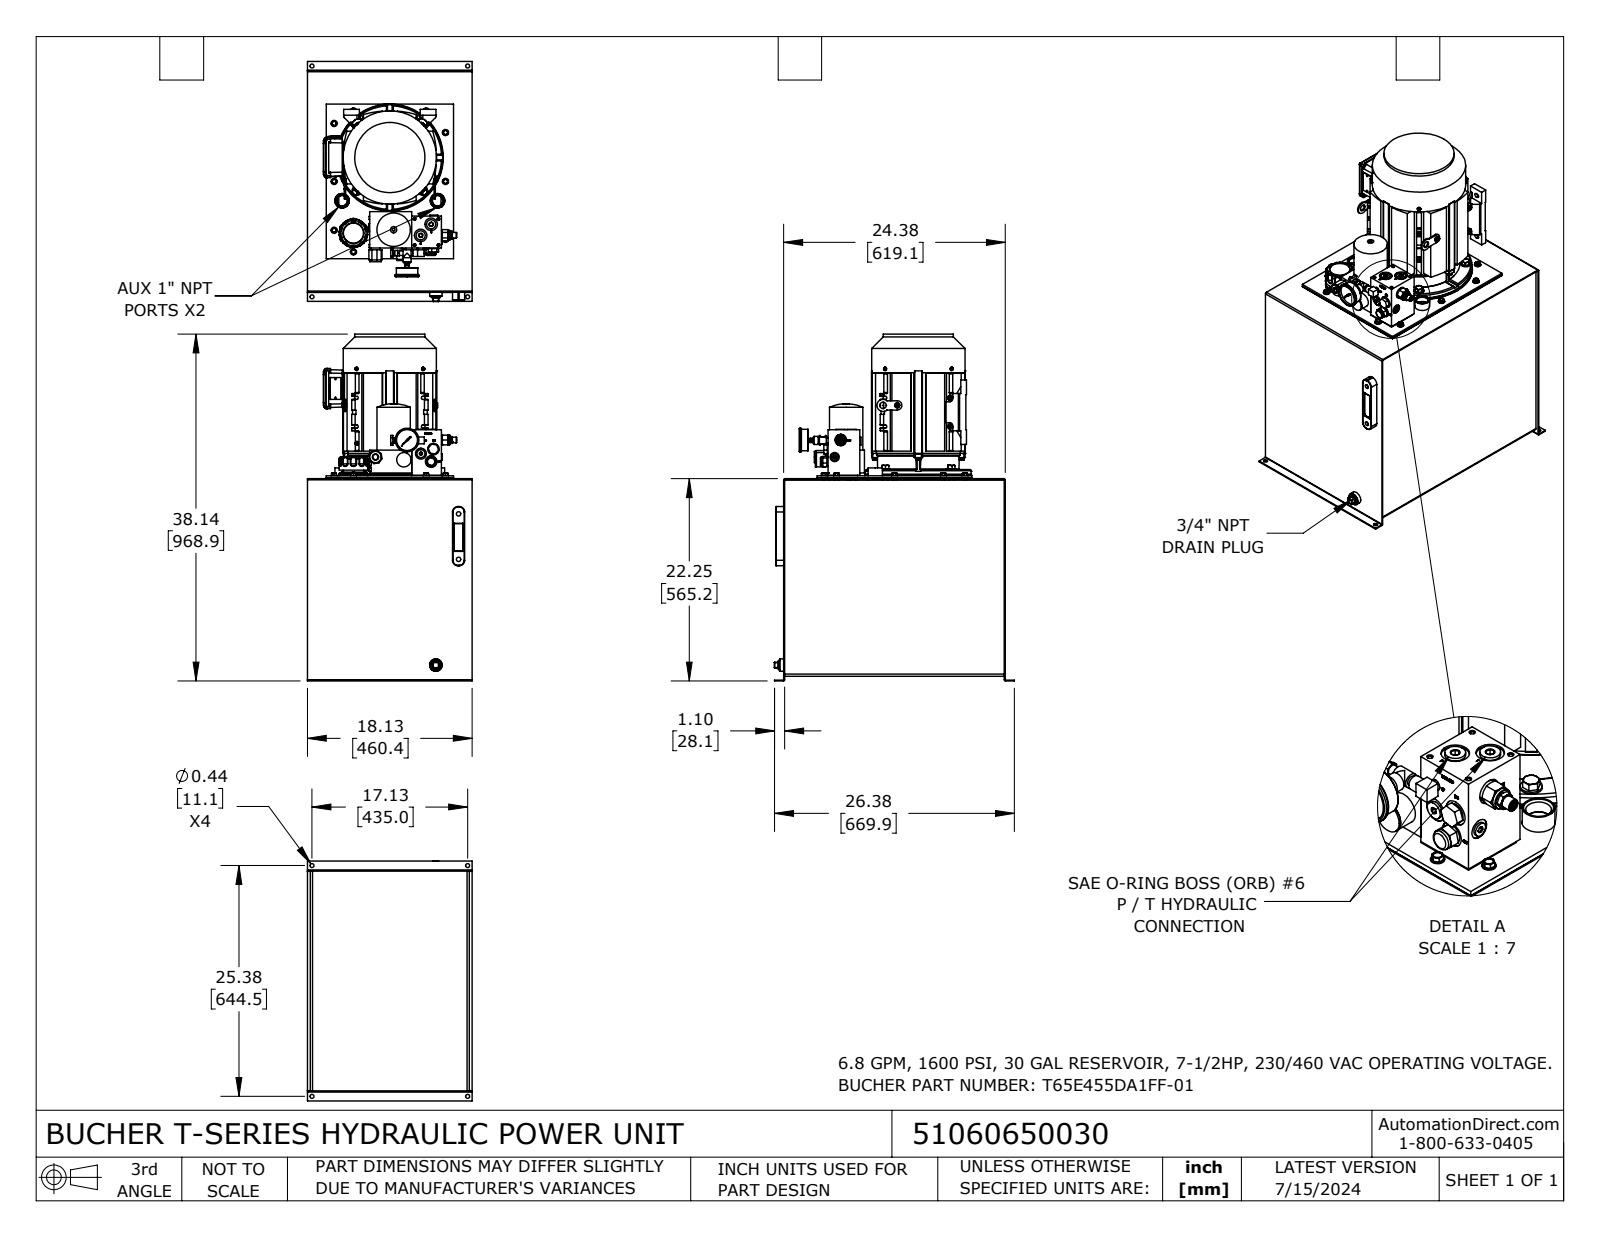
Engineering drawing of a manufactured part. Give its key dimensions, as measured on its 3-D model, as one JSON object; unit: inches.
{"part_name": "51060650030", "step_written_by": "SolidWorks 2023 (CONFIG_CONTROL_DESIGN)", "units": "inches", "bodies": {"solids": 112, "faces": 5067, "planar": 2486, "cylindrical": 1682, "other": 899}, "overall_size": [38.144, 26.4, 18.125], "volume_in3": 1748, "surface_area_in2": 7698, "round_holes": [[0.437, 19], [0.236, 11], [0.5, 11], [0.197, 10], [0.563, 10], [0.315, 9], [0.201, 8], [0.268, 8], [0.12, 6], [0.19, 6], [0.531, 6], [0.807, 5]], "round_bosses_or_shafts": [[0.676, 10], [0.313, 10], [0.551, 9], [0.472, 9], [0.373, 6], [0.5, 5], [0.25, 5], [1.062, 4]], "partial_cylinders_radius": [[0.02, 188], [0.079, 68], [0.039, 52], [0.25, 36], [0.063, 20], [0.118, 20], [0.375, 16], [0.05, 13]], "face_to_face_distances": [0.104, 0.105, 17.395, 24.27, 21.635, 17.5, 17.291, 24.375, 24.166, 21.739], "hole_center_spacings": [3.15, 3.469, 1.441, 1.442, 2.497, 6.232, 8.297, 0.78]}
